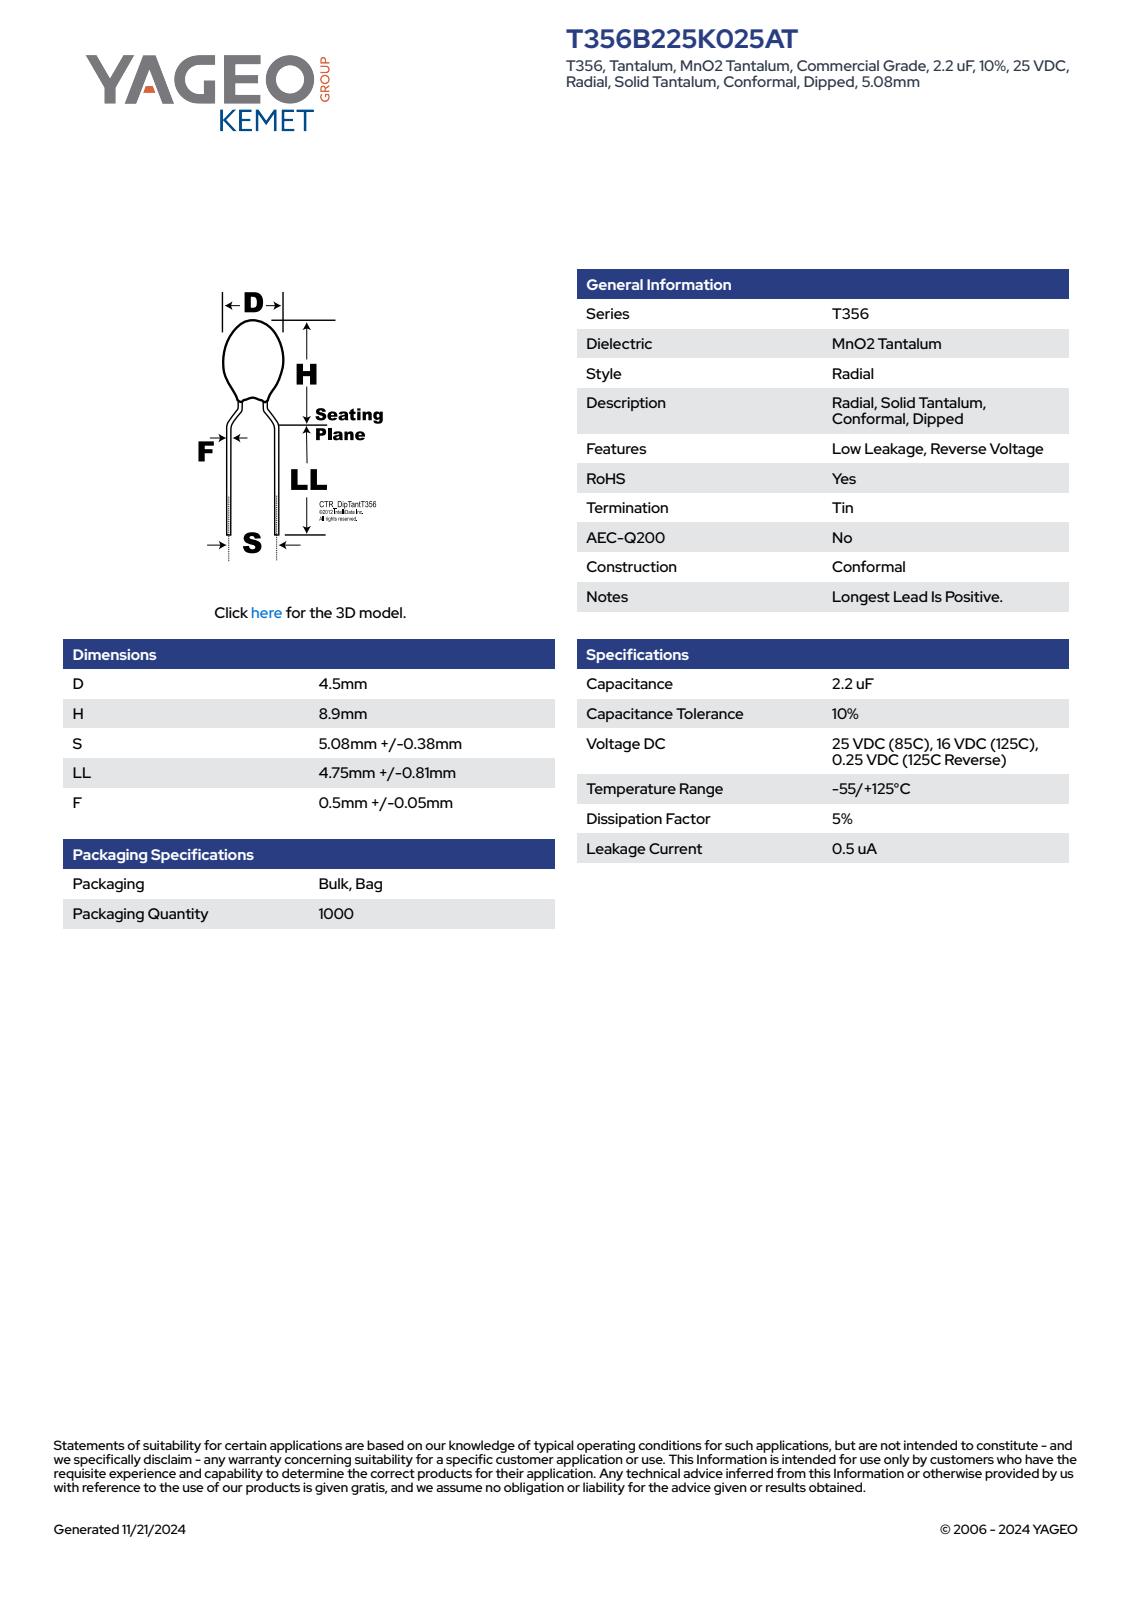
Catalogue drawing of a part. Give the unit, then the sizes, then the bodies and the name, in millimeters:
Units: millimetres
Overall size (bounding box): 14.46 × 5.63 × 4.5
Round bosses / shafts (diameter × count): ⌀0.55 ×6, ⌀4.5 ×1
Partial cylindrical surfaces — rounded edges, fillets, slot ends (radius × count): R2.24 ×1
Main face-to-face distances: 6.21, 8.25, 14.46, 12.3, 4.05, 2.16, 11.6, 3.35, 0.7, 2.86
Volume: 94 mm³ · Surface area: 136 mm²
Bodies: 1 solid, 100 faces (27 planar, 18 cylindrical, 55 other)
Part name (STEP PRODUCT): CTR_T356_D4.5H8.9S5.08LL5.56F0.55
STEP written by: SolidWorks 2014 (AUTOMOTIVE_DESIGN)
